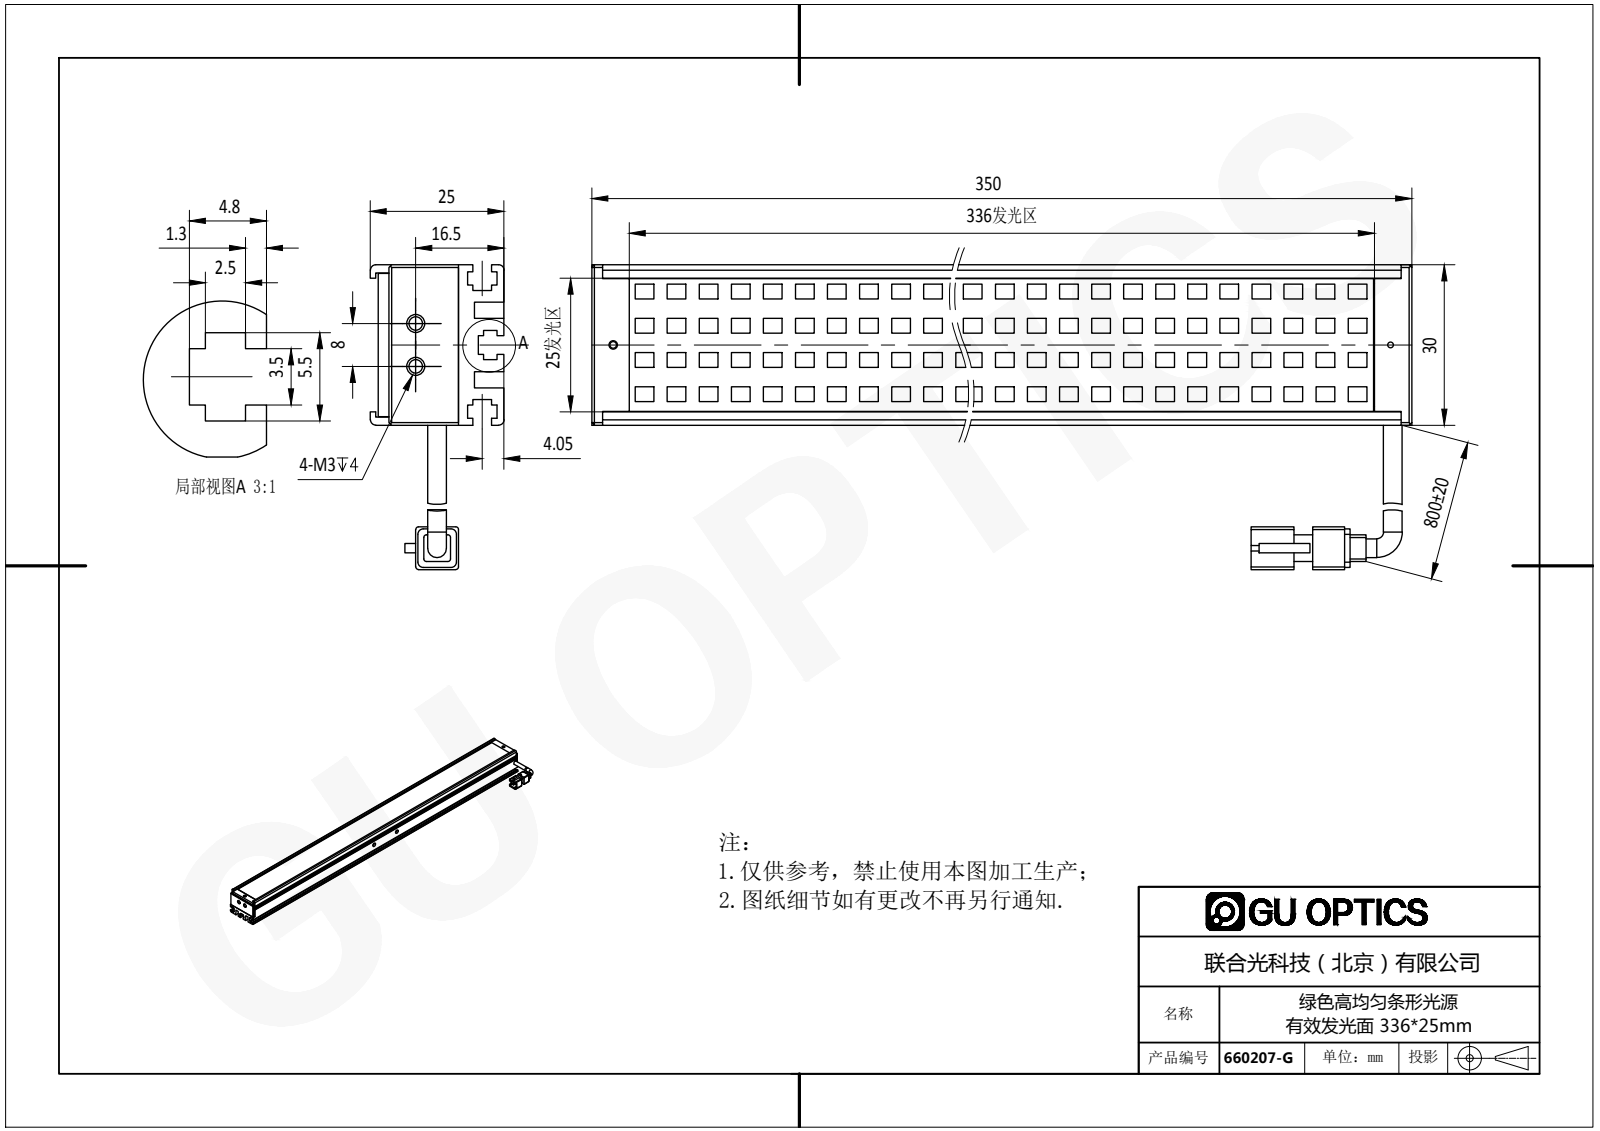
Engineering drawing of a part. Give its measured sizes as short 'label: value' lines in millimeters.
name: 660207-G
written by: SolidWorks 2016 (AUTOMOTIVE_DESIGN)
unit: mm
bodies: 6 solids, 1564 faces (1378 planar, 83 cylindrical, 103 other)
size: 350 × 57 × 25
volume: 118 035 mm³; area: 120 531 mm²
holes: 5× ⌀1.6, 2× ⌀1.5, 2× ⌀1.7, 2× ⌀2.5, 2× ⌀2.8, 2× ⌀3, 1× ⌀1.1, 1× ⌀1.25, 1× ⌀2
bosses: 2× ⌀3.5
rounds: 12× R1, 8× R0.5, 1× R1.65
face distances: 1, 13, 2, 2.5, 3, 27.5, 9.5, 4.5, 12, 15.1
hole spacings: 342, 7, 156, 156.14, 186, 186.12, 342.07, 8
